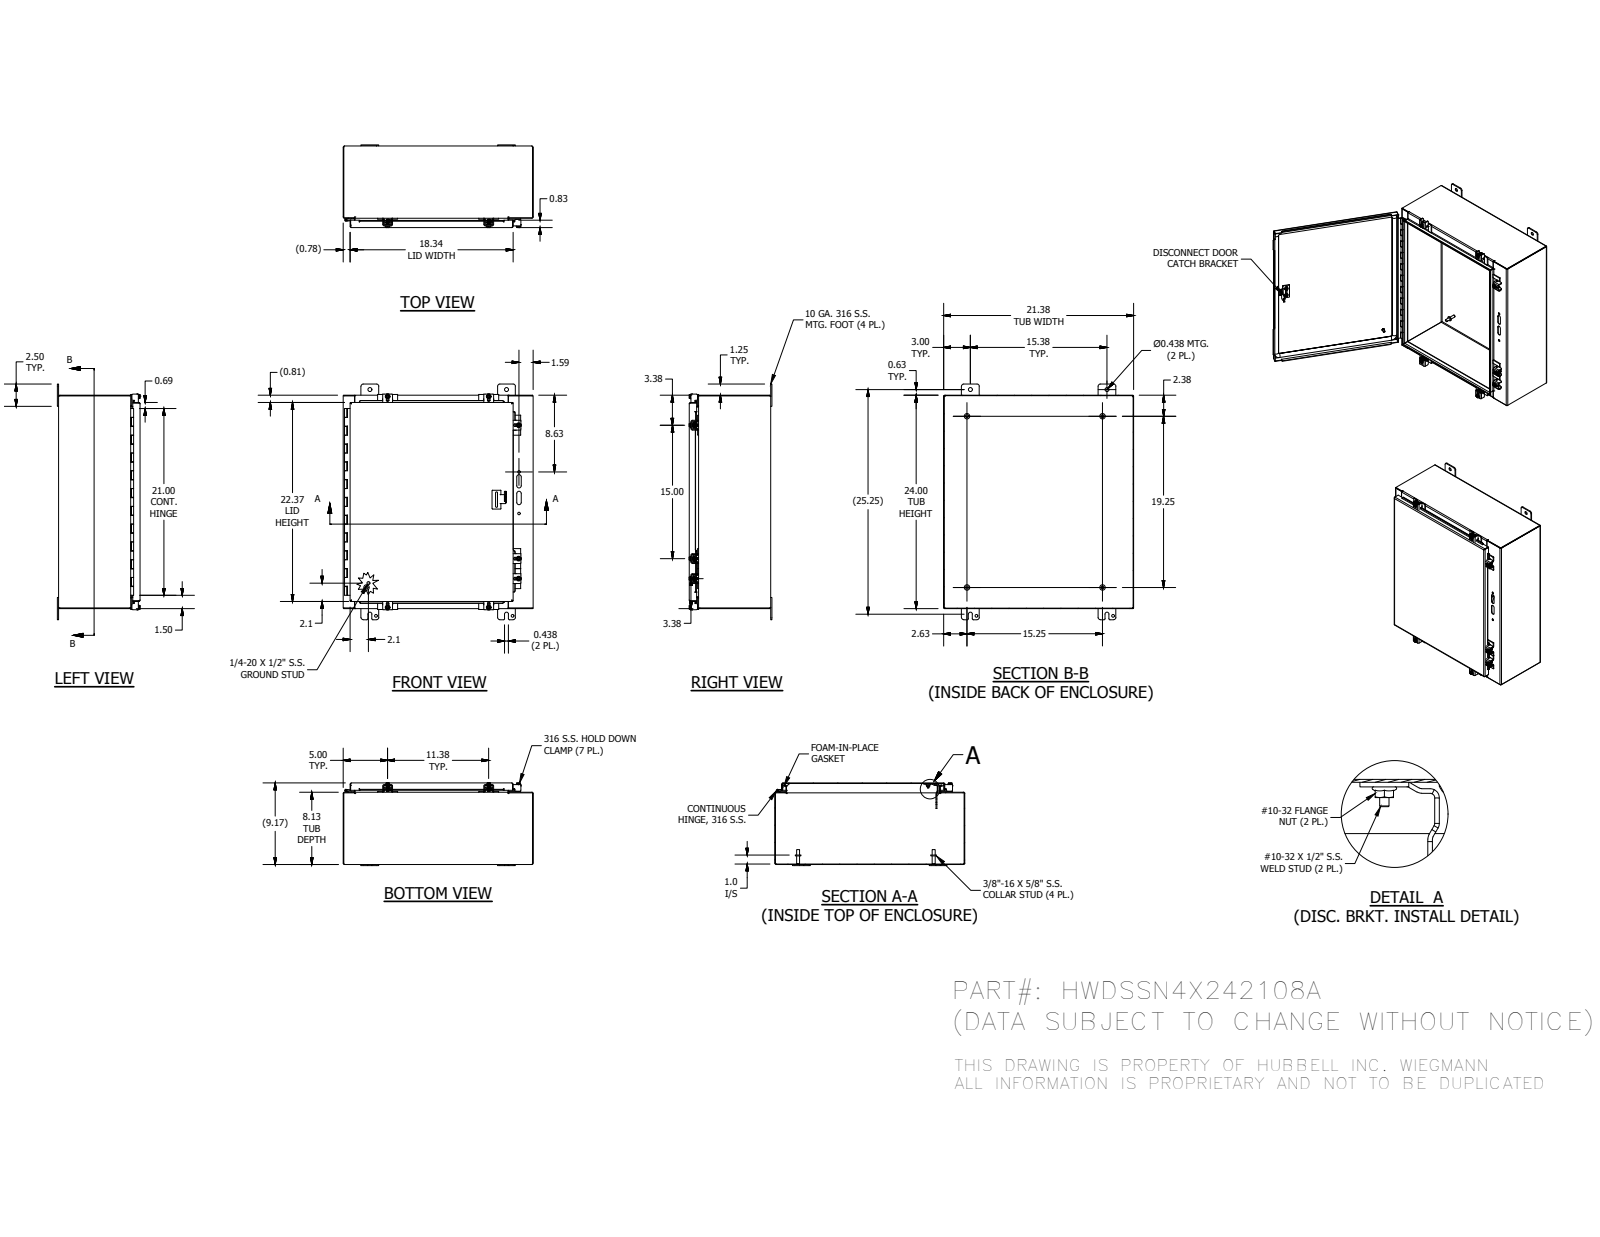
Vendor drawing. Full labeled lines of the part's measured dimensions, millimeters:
Part name (STEP PRODUCT): SSN4X242108ABKP; 38859; 34839; 32874-24T (+8 more)
STEP written by: Autodesk Inventor 2016 (AUTOMOTIVE_DESIGN)
Units: millimetres
Bodies: 20 solids, 754 faces (439 planar, 227 cylindrical, 88 other)
Overall size (bounding box): 673.1 × 542.92 × 236.22
Volume: 2 169 000 mm³ · Surface area: 2 671 000 mm²
Round holes (diameter × count): ⌀7.95 ×4, ⌀11.13 ×4, ⌀3.17 ×2, ⌀3.96 ×2, ⌀7.14 ×2
Round bosses / shafts (diameter × count): ⌀15.88 ×4, ⌀8.38 ×4, ⌀8.56 ×3, ⌀6.35 ×2, ⌀4.83 ×2, ⌀3.05 ×1
Partial cylindrical surfaces — rounded edges, fillets, slot ends (radius × count): R2.38 ×28, R3.88 ×23, R6.35 ×21, R3.17 ×11, R0.25 ×8, R1.92 ×8, R4.76 ×5, R0.4 ×4
Main face-to-face distances: 1.5, 231.54, 230.04, 233.04, 608.1, 1.49, 204.88, 26.66, 542.92, 541.42
Hole centre spacings: 390.52, 40.46, 409.6, 573.38, 609.6, 609.61, 646.34, 723.96
